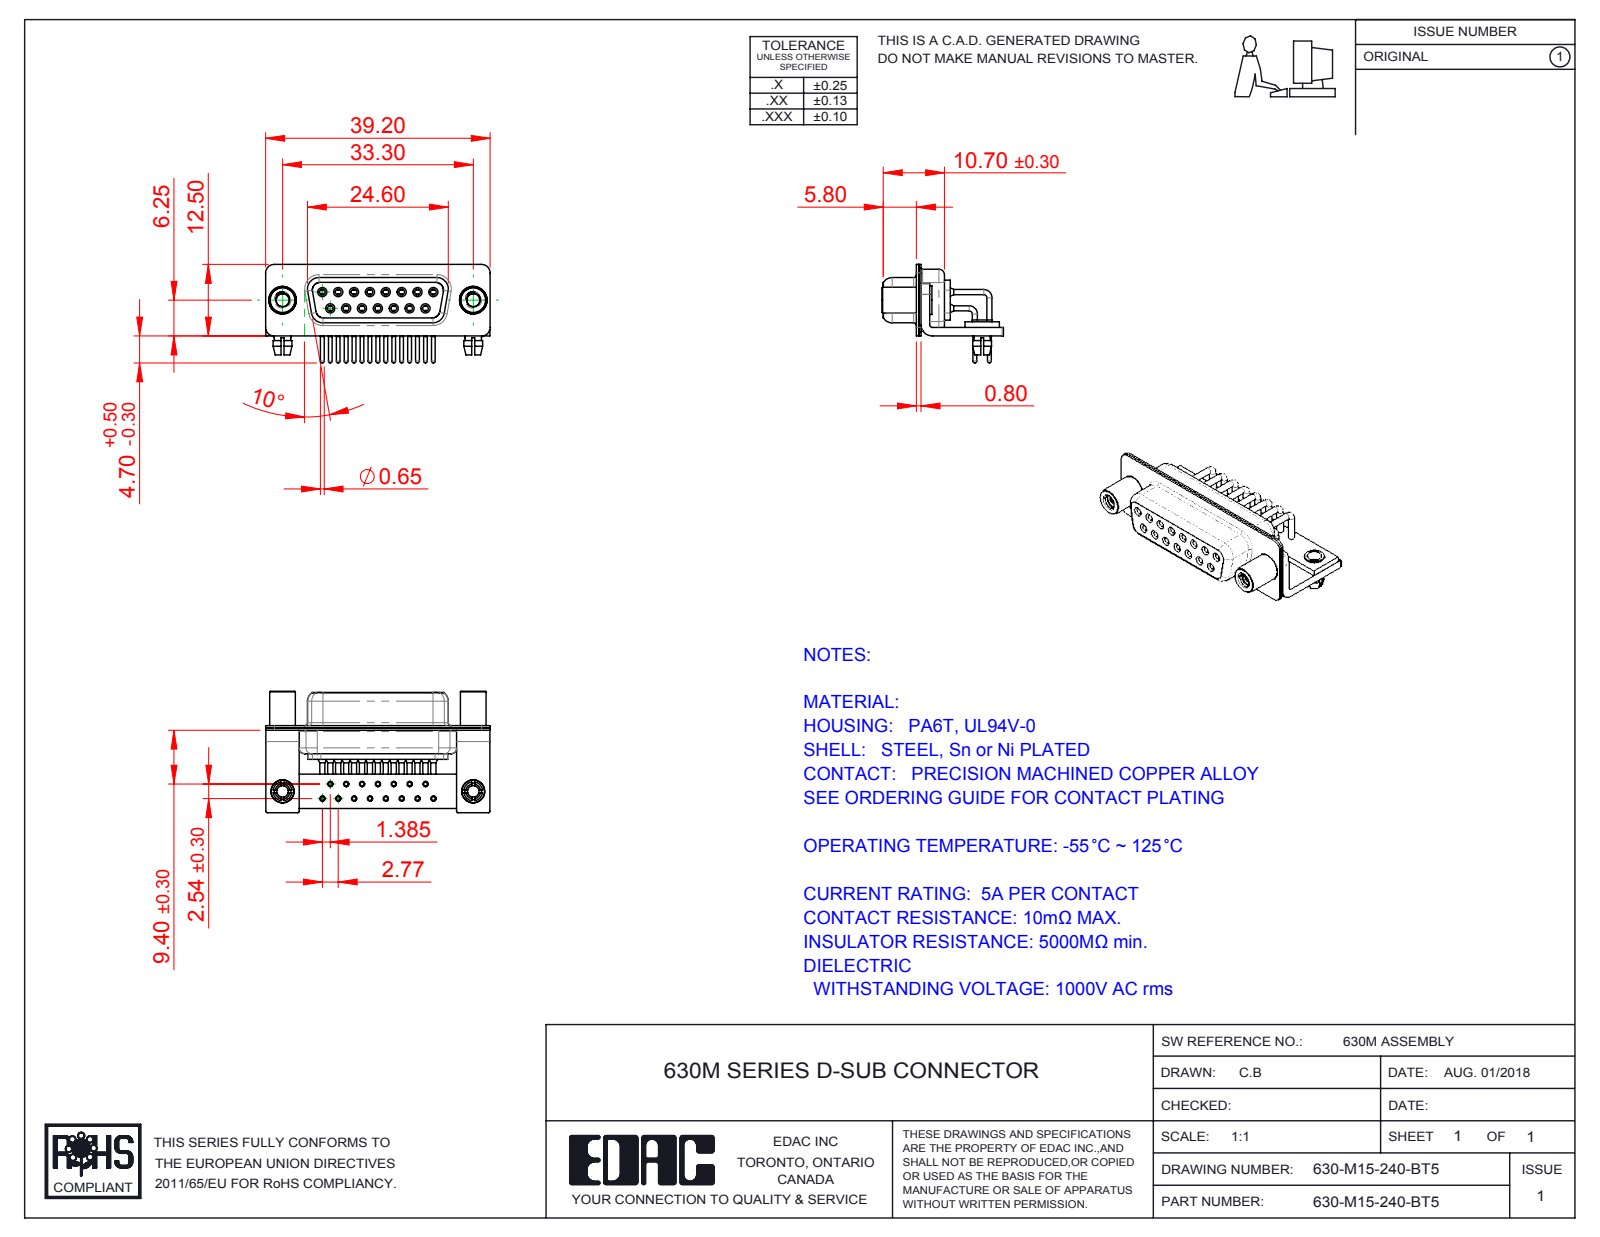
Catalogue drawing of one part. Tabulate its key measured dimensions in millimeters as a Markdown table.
| quantity | value |
| --- | --- |
| part name | 630M Contact Row 1; 630M Contact Row 2; 630-M15-240-BT5; 630M 4-40 Threaded Standoff (+6 more) |
| STEP written by | SolidWorks 2016 (CONFIG_CONTROL_DESIGN) |
| units | millimeters |
| bodies | 25 solids, 1296 faces (368 planar, 608 cylindrical, 320 other) |
| overall size | 39.2 × 21.2 × 17.2 |
| volume | 3 217 mm³ |
| surface area | 8 278 mm² |
| round holes (diameter × count) | 2 × 17, 0.9 × 15, 1 × 15, 1.1 × 15, 1.7 × 15, 1.8 × 15, 2.26 × 2, 2.5 × 2, 3.2 × 2, 4 × 2, 4.8 × 2 |
| round bosses / shafts (diameter × count) | 0.9 × 27, 1.6 × 15, 1.5 × 15, 0.65 × 15, 5 × 2, 4.9 × 2, 4.5 × 2, 4 × 2 |
| partial cylindrical surfaces (radius × count) | 0.25 × 16, 1.5 × 16, 2 × 13, 1.35 × 8, 1.6 × 8, 0.5 × 5, 0.6 × 4, 0.65 × 4 |
| main face-to-face distances | 0.4, 2.3, 1.9, 0.8, 1.5, 9.35, 1, 1.45, 8.95, 0.85 |
| hole center spacings | 2.77, 5.54, 8.31, 3.16, 4.87, 11.08, 2.89, 7.37 |
